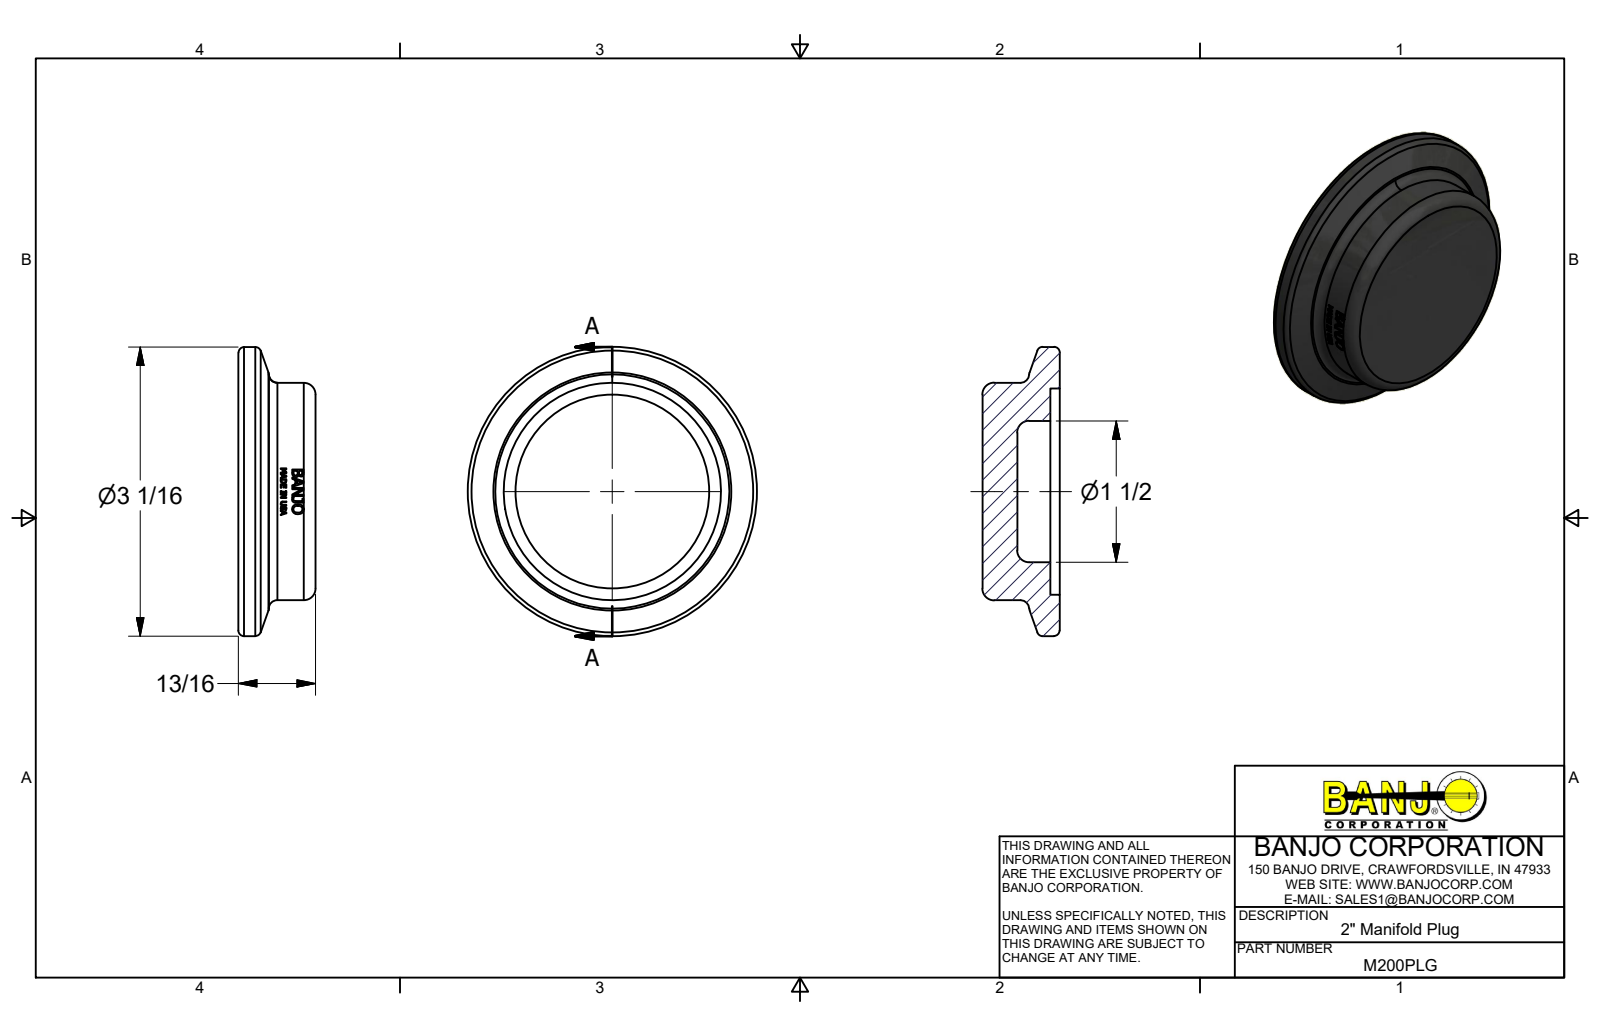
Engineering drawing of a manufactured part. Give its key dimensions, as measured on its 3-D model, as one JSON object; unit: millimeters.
{"part_name": "M200PLG; M200PLGU", "step_written_by": "Autodesk Inventor 2017 (AUTOMOTIVE_DESIGN)", "units": "millimeters", "bodies": {"solids": 1, "faces": 331, "planar": 167, "cylindrical": 35, "other": 129}, "overall_size": [77.98, 77.98, 20.83], "volume_mm3": 54740, "surface_area_mm2": 14245, "round_holes": [[38.1, 1], [55.63, 1]], "round_bosses_or_shafts": [[77.98, 1], [58.62, 1]], "partial_cylinders_radius": [[28.55, 1]], "face_to_face_distances": [20.83, 18.29, 2.54, 9.4, 8.89, 11.43, 1.2, 4.96, 2.89, 0.51]}
